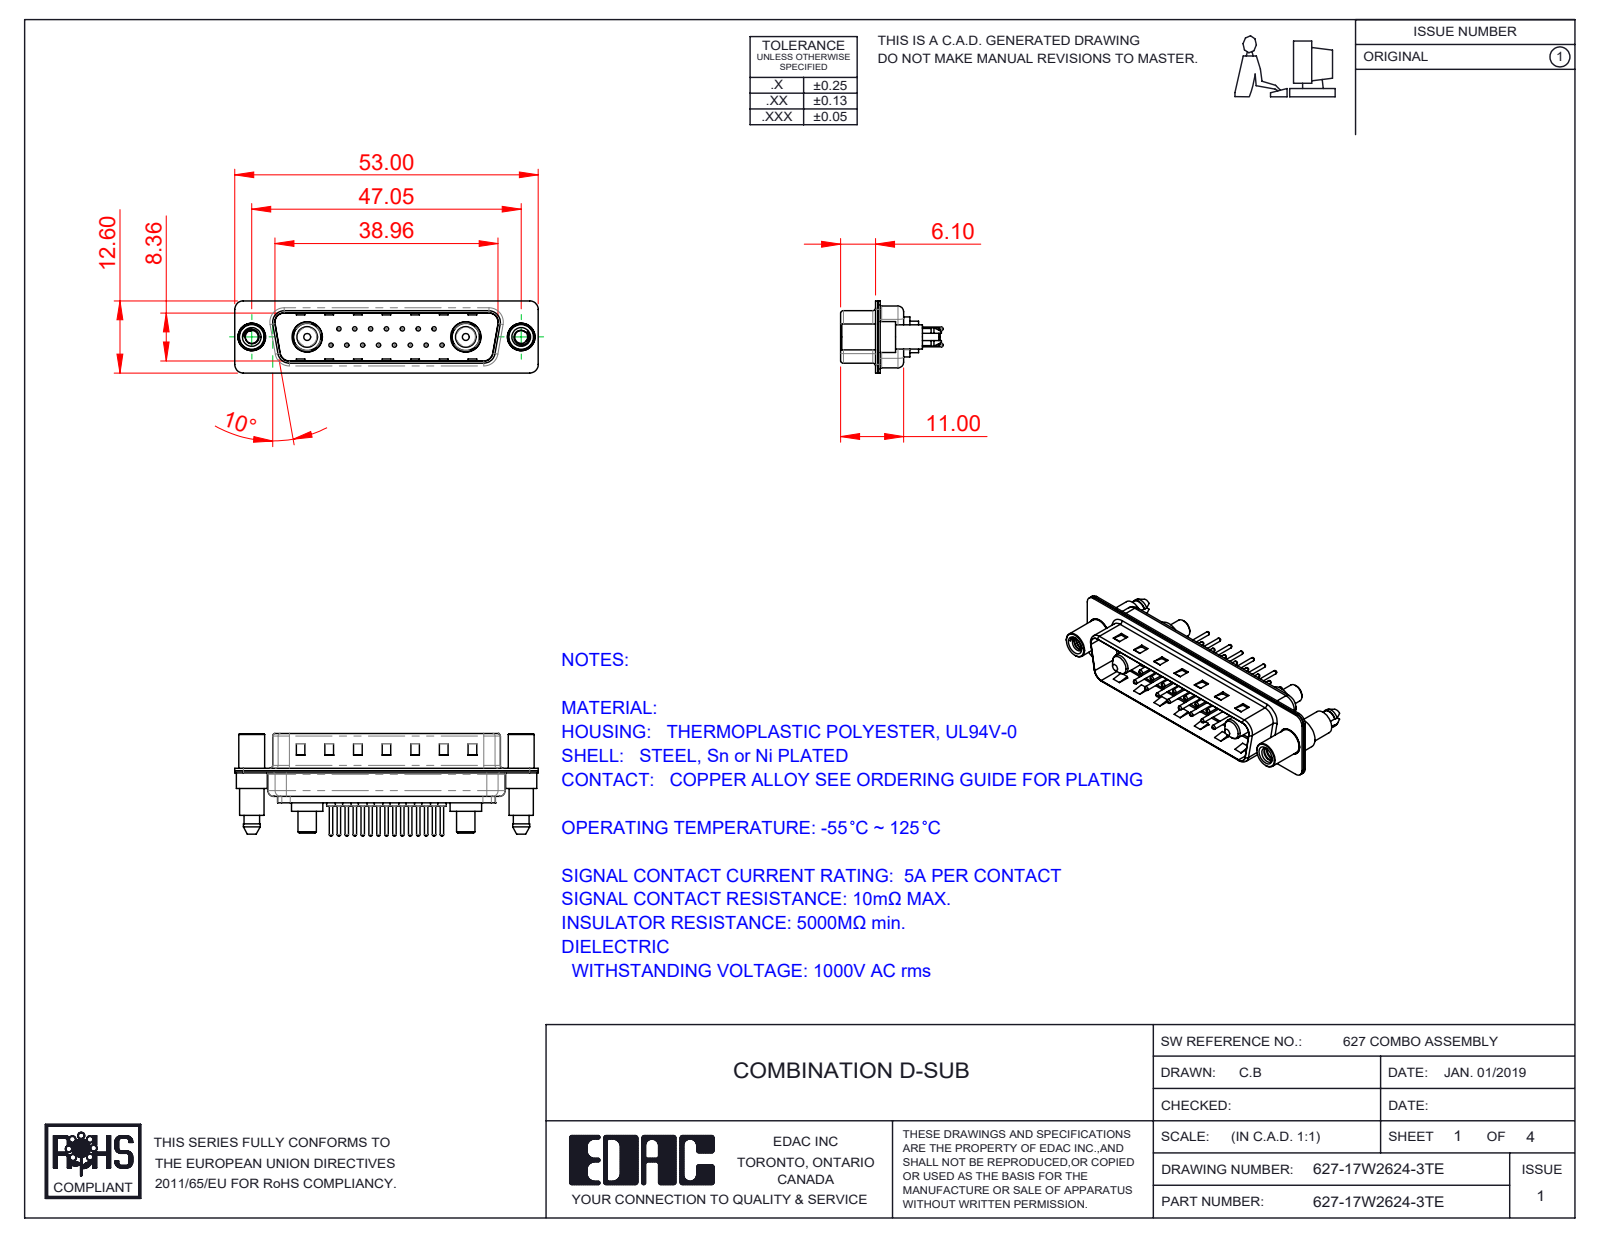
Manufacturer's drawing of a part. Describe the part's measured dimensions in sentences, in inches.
The part is named "627-17W2624-3TE; 627Combo Housing_17W2; 627Combo Threaded Standoff and Boardlock_6; 627Combo Shell Front_25 Contacts (+5 more)". Its 3-D file was written by "SolidWorks 2016 (CONFIG_CONTROL_DESIGN)". It is 24 solids with 1066 faces: 314 planar, 417 cylindrical and 335 other. Overall it measures 2.087 by 0.705 by 0.496 inches. Its volume is 0.196 cubic inches and its surface area 11.26 square inches. Round holes: 15 of diameter 0.03, 15 of diameter 0.063, 15 of diameter 0.079, 2 of diameter 0.089, 2 of diameter 0.157, 2 of diameter 0.189, 2 of diameter 0.191, 2 of diameter 0.209. Round bosses or shafts: 15 of diameter 0.059, 15 of diameter 0.024, 2 of diameter 0.217, 2 of diameter 0.213, 2 of diameter 0.205, 2 of diameter 0.193, 2 of diameter 0.187, 2 of diameter 0.177. Partial cylindrical surfaces (rounded edges, fillets, slot ends): 18 of radius 0.059, 12 of radius 0.079, 10 of radius 0.063, 8 of radius 0.02, 4 of radius 0.01, 4 of radius 0.024, 4 of radius 0.026, 4 of radius 0.035. The main face-to-face distances are 0.016, 0.032, 0.377, 0.345, 0.059, 0.22, 0.205, 0.031, 0.236, 0.048. The hole center spacings are 0.124, 0.109, 0.218, 0.327, 0.198, 0.295, 0.436, 0.198.
